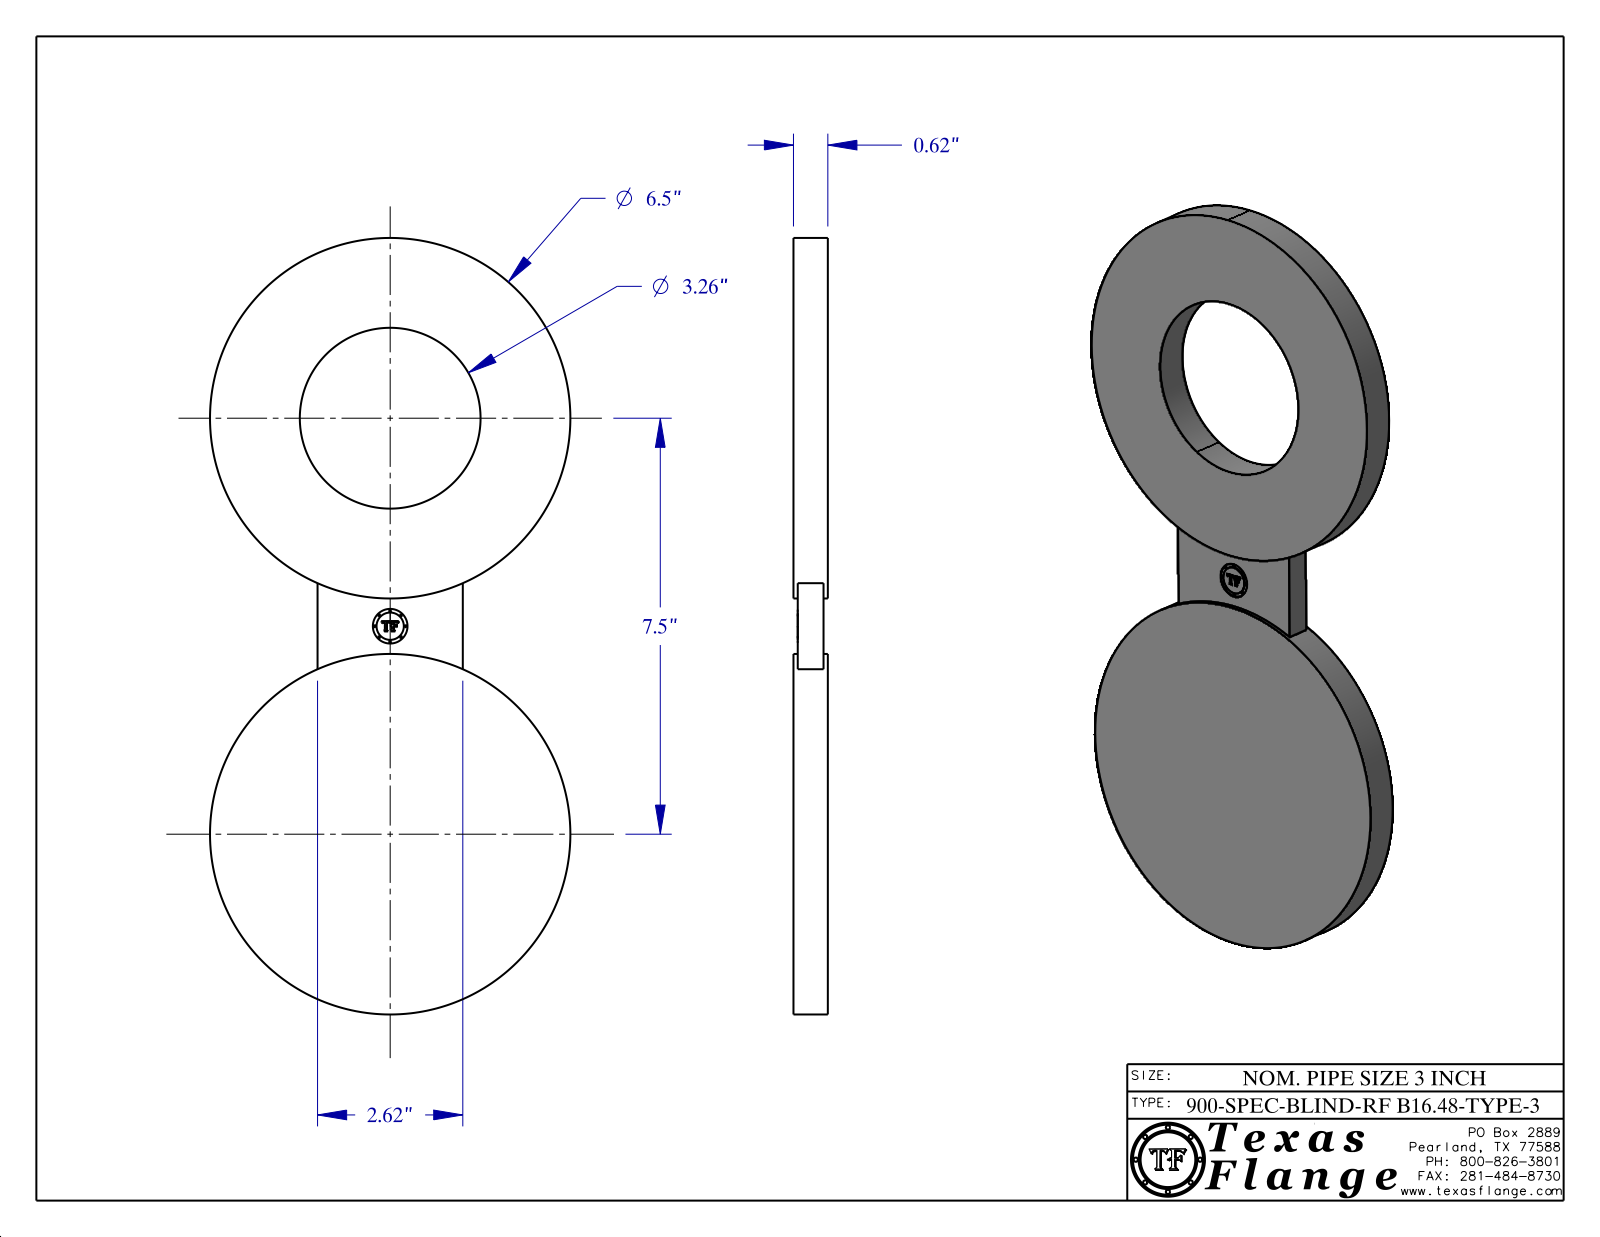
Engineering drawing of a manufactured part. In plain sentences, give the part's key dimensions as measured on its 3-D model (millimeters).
The part is named "3-900-SPEC-BLIND-RF-B16.48-TYPE-3". Its 3-D file was written by "CATIA V5 STEP AP214 (AUTOMOTIVE_DESIGN)". It is 1 solid with 399 faces: 373 planar, 26 cylindrical and 0 other. Overall it measures 355.6 by 165.1 by 15.7 millimeters. Its volume is 613 000 cubic millimeters and its surface area 98 640 square millimeters. Round holes: 1 of diameter 15.9, 1 of diameter 82.8. Round bosses or shafts: 8 of diameter 1, 2 of diameter 165.1, 1 of diameter 12.5. The main face-to-face distances are 15.7, 2, 13.8, 11.8, 66.5, 13.4, 11.4, 0.4, 2.4, 31.7. The hole center spacings are 95.3.
